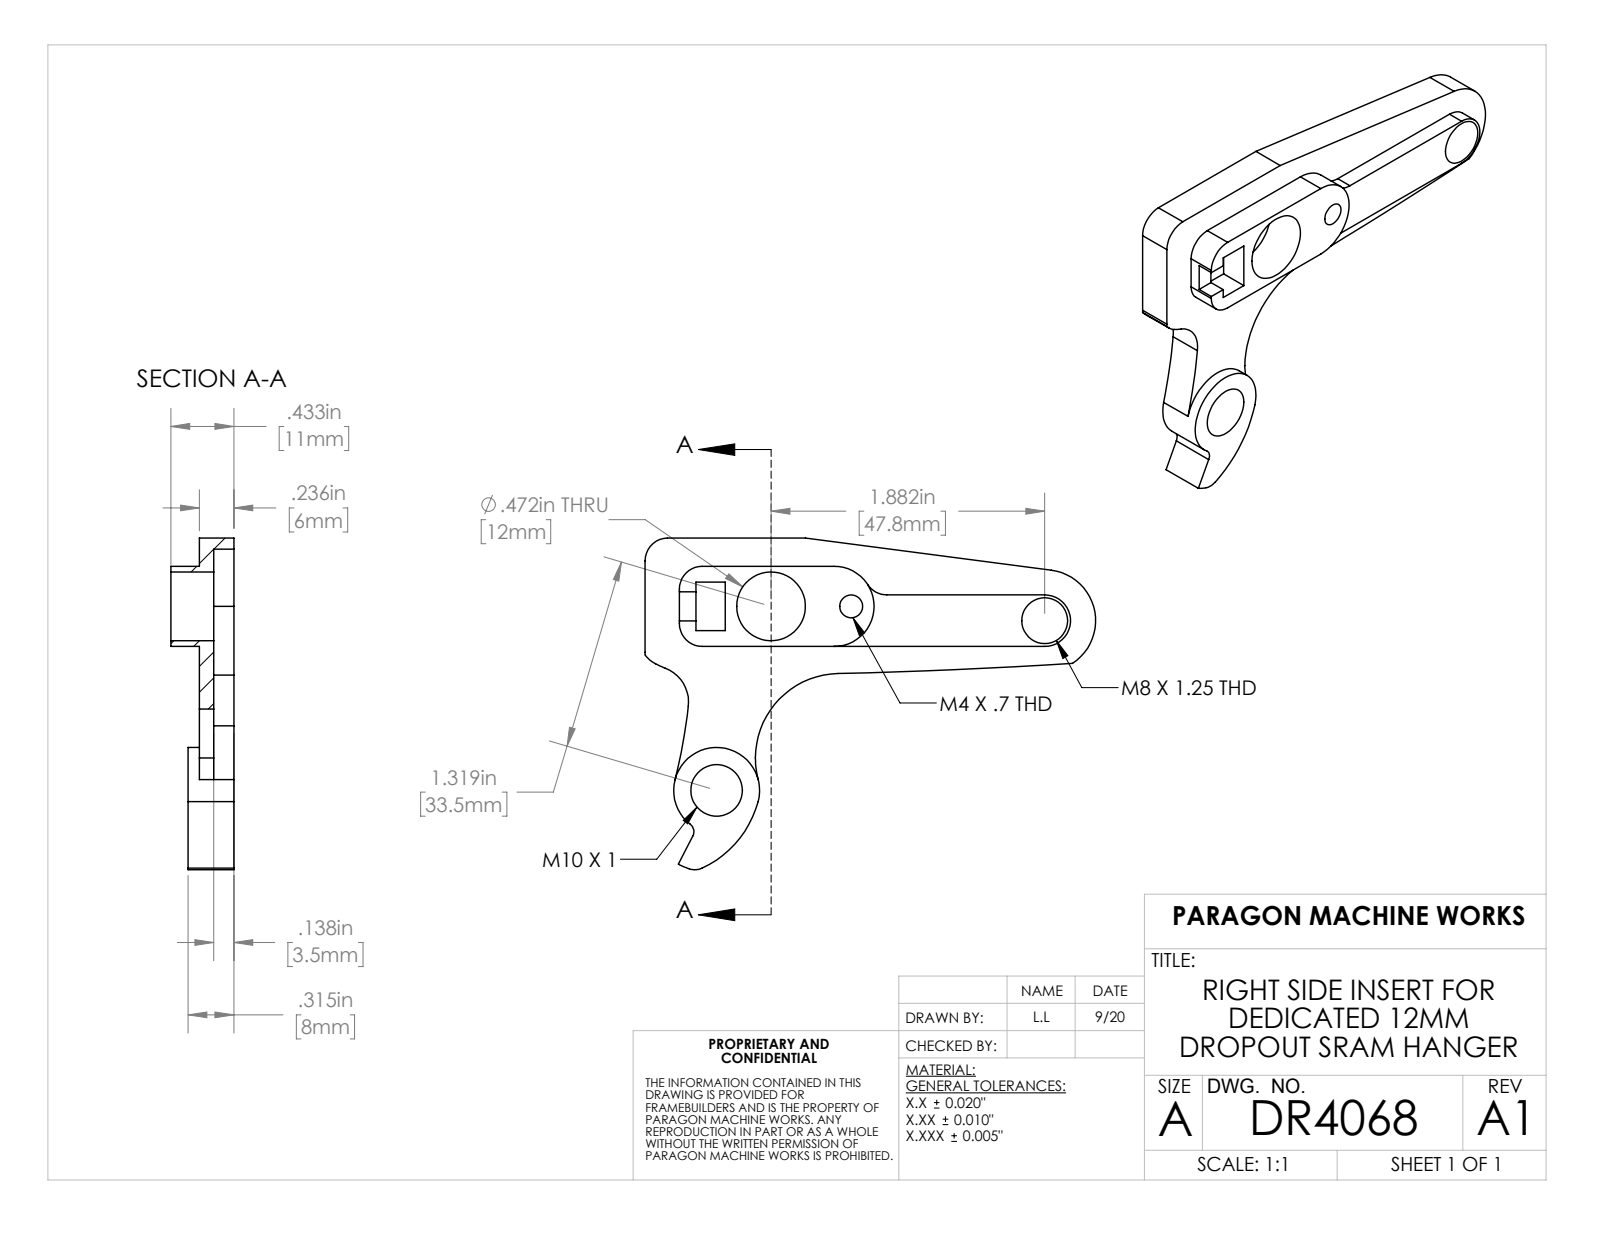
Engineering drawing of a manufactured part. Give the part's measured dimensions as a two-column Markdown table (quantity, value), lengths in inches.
| quantity | value |
| --- | --- |
| part name | DR4068 |
| STEP written by | SolidWorks 2020 (AUTOMOTIVE_DESIGN) |
| units | inches |
| bodies | 1 solid, 62 faces (27 planar, 35 cylindrical, 0 other) |
| overall size | 3.098 × 2.28 × 0.433 |
| volume | 0.736 in³ |
| surface area | 10.88 in² |
| round holes (diameter × count) | 0.157 × 1, 0.315 × 1, 0.354 × 1, 0.472 × 1 |
| partial cylindrical surfaces (radius × count) | 0.157 × 5, 0.394 × 2, 0.065 × 1, 0.118 × 1, 0.177 × 1, 0.206 × 1, 0.25 × 1, 0.276 × 1 |
| main face-to-face distances | 0.236, 0.079, 0.118, 0.098, 0.138, 0.197, 0.354, 0.295, 0.433, 0.217 |
| hole center spacings | 0.551, 1.319, 1.334, 1.567, 1.884, 2.539 |
